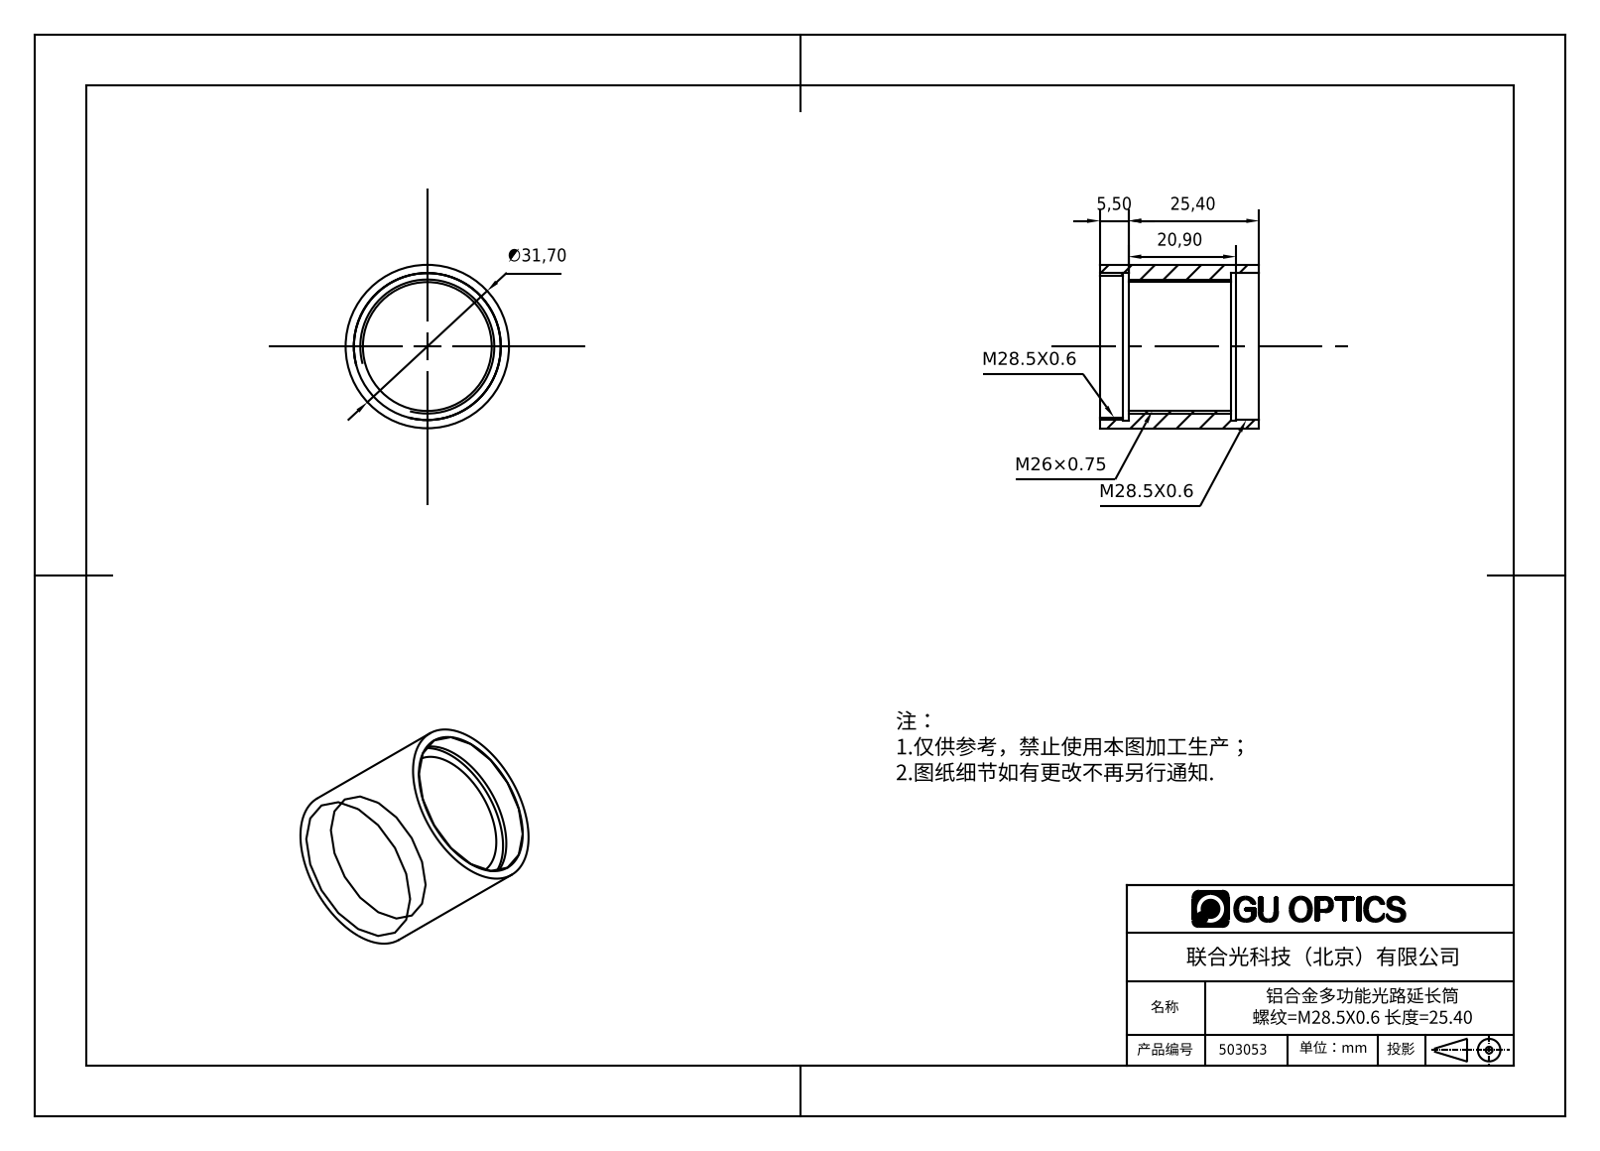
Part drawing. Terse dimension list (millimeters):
name: 503053
written by: SolidWorks 2016 (AUTOMOTIVE_DESIGN)
unit: mm
bodies: 1 solid, 18 faces (6 planar, 12 cylindrical, 0 other)
size: 31.7 × 31.7 × 30.9
volume: 7 782 mm³; area: 6 333 mm²
holes: 1× ⌀25, 1× ⌀27.5, 1× ⌀28.5, 1× ⌀28.7
bosses: 1× ⌀31.7
face distances: 25.4, 5.5, 19.9, 30.9, 4.5, 26.4, 1, 20.9, 21.9
